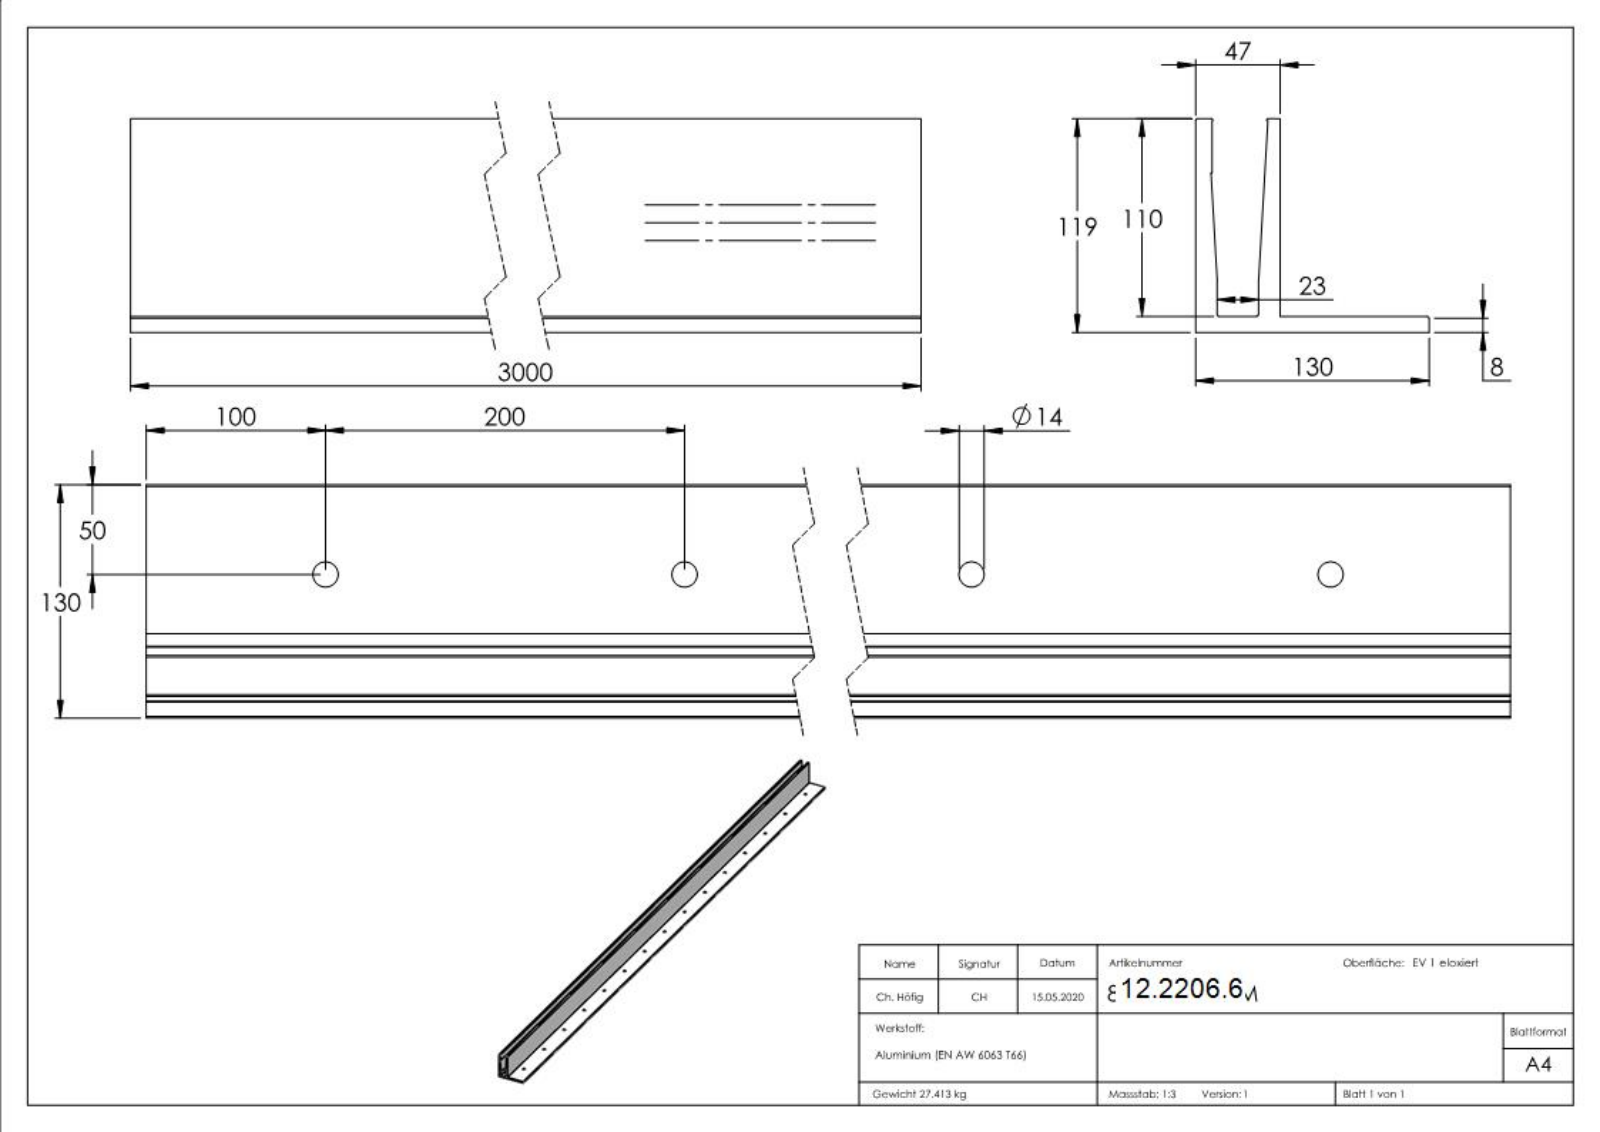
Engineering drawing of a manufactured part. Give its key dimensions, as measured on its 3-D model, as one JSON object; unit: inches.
{"part_name": "80700-ALU-3M", "step_written_by": "SolidWorks 2015 (CONFIG_CONTROL_DESIGN)", "units": "inches", "bodies": {"solids": 1, "faces": 303, "planar": 152, "cylindrical": 38, "other": 113}, "overall_size": [118.11, 5.118, 4.685], "volume_in3": 619.4, "surface_area_in2": 3314, "round_holes": [[0.551, 15]], "partial_cylinders_radius": [[0.039, 4], [0.026, 2], [0.01, 1]], "face_to_face_distances": [1.85, 0.354, 0.472, 1.378, 0.362, 1.488, 0.11, 1.016, 0.906, 4.685], "hole_center_spacings": [7.874, 15.748, 23.622, 31.496, 39.37, 47.244, 55.118, 62.992]}
